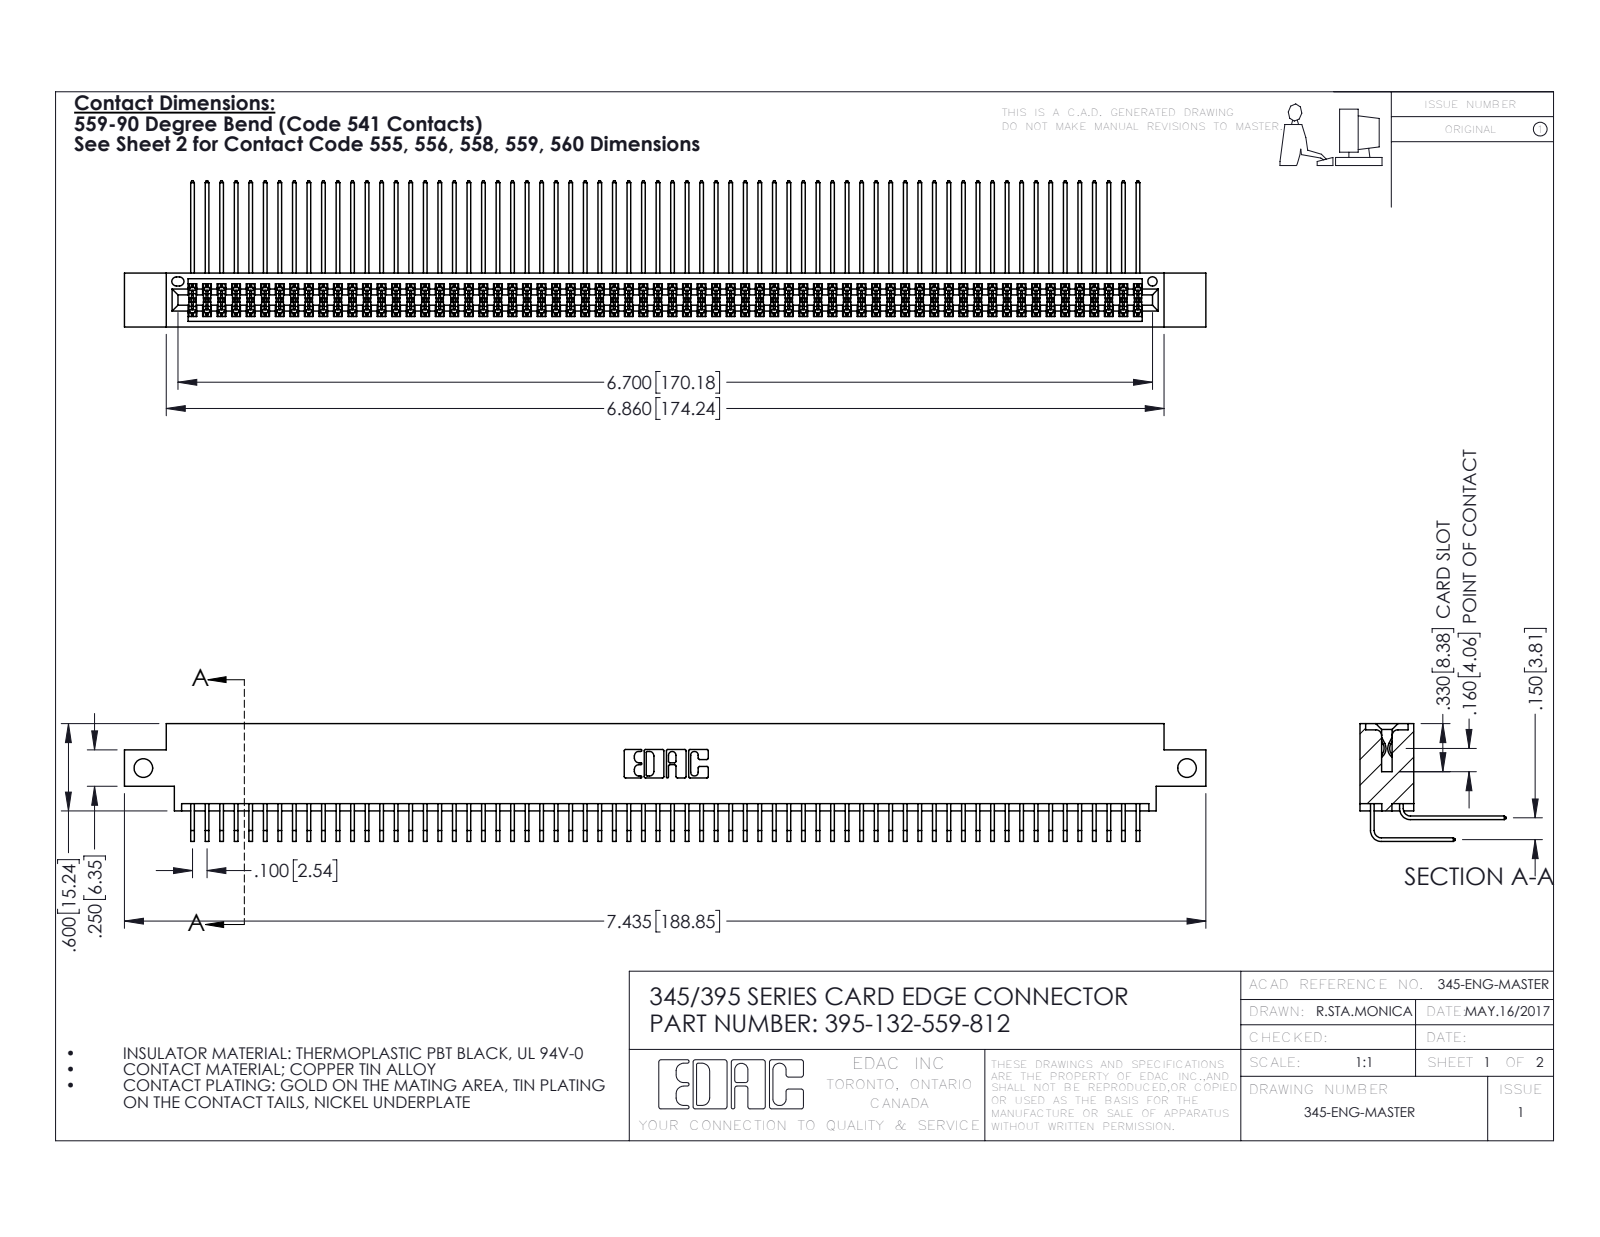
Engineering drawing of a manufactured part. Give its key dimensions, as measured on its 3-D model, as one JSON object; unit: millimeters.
{"part_name": "345 Part_0.170 Offset - Side Mount; 345-292-001_559 Tail - 2; 345-292-001_558 559 Tail - 1; 395-132-559-812", "step_written_by": "SolidWorks 2016 (CONFIG_CONTROL_DESIGN)", "units": "millimeters", "bodies": {"solids": 133, "faces": 6994, "planar": 4704, "cylindrical": 2290, "other": 0}, "overall_size": [188.8, 25.5, 20.5], "volume_mm3": 19120, "surface_area_mm2": 32330, "round_holes": [[3.3, 2], [1.6, 1]], "partial_cylinders_radius": [[0.2, 198], [0.3, 22], [0.2, 6], [0.8, 6], [0.7, 3], [0.4, 2], [0.5, 2], [0.6, 2]], "face_to_face_distances": [1.8, 7.6, 9.4, 5.1, 2.5, 6.9, 0.6, 5.7, 4.4, 3.8], "hole_center_spacings": [182.2]}
